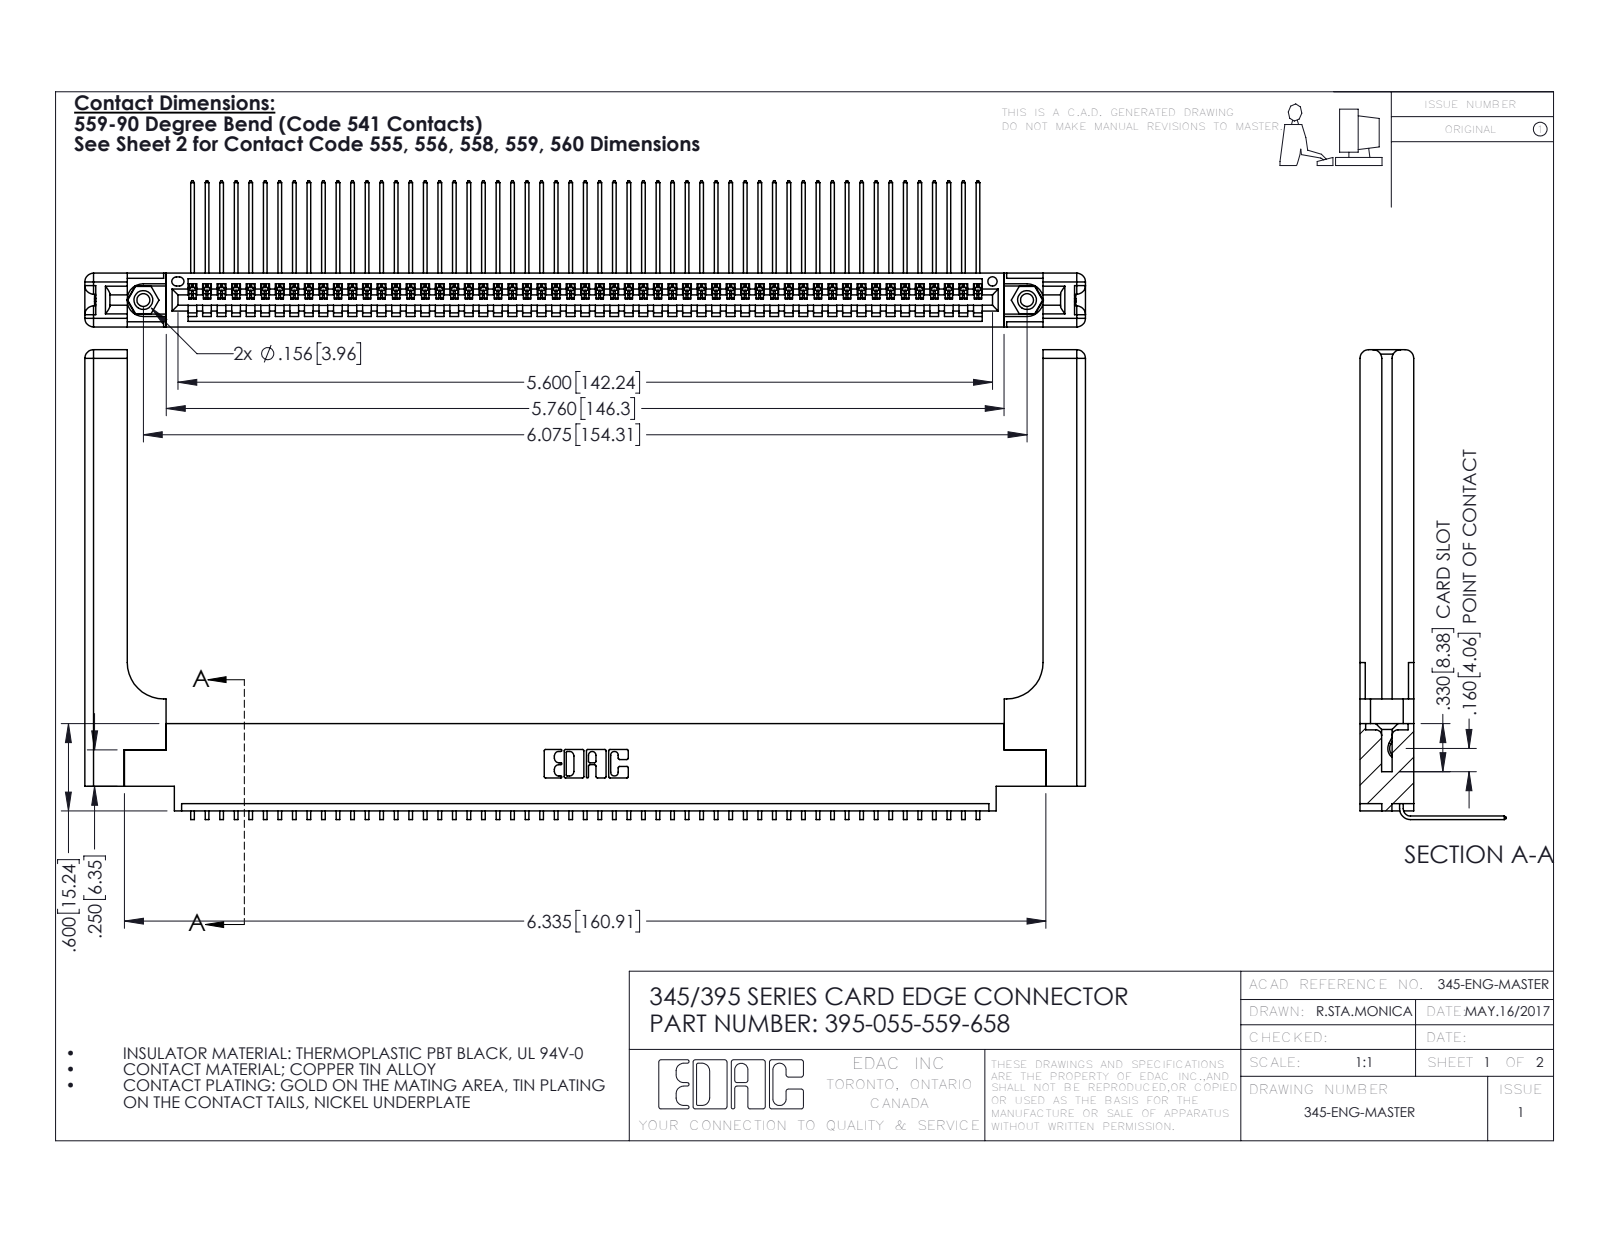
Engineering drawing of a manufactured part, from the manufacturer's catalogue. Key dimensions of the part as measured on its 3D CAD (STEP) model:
Part name (STEP PRODUCT): 345-220-058_345-220-058; 345-292-001_558 559 Tail - 1; 345 Part_0.170 Offset - 0.156 Dia-TH; 395-055-559-658 (+1 more)
STEP written by: SolidWorks 2016 (CONFIG_CONTROL_DESIGN)
Units: inches
Bodies: 60 solids, 3686 faces (2542 planar, 1084 cylindrical, 60 other)
Overall size (bounding box): 6.879 × 3.229 × 1.005
Volume: 1.542 in³ · Surface area: 44.91 in²
Round holes (diameter × count): ⌀0.089 ×2, ⌀0.125 ×2, ⌀0.156 ×2, ⌀0.064 ×1
Round bosses / shafts (diameter × count): ⌀0.155 ×2
Partial cylindrical surfaces — rounded edges, fillets, slot ends (radius × count): R0.006 ×110, R0.01 ×22, R0.06 ×16, R0.007 ×6, R0.031 ×6, R0.026 ×3, R0.03 ×2, R0.031 ×2
Main face-to-face distances: 0.37, 0.072, 0.298, 0.098, 0.272, 0.025, 0.2, 0.225, 0.148, 0.15
Hole centre spacings: 0.27, 5.839, 6.075
